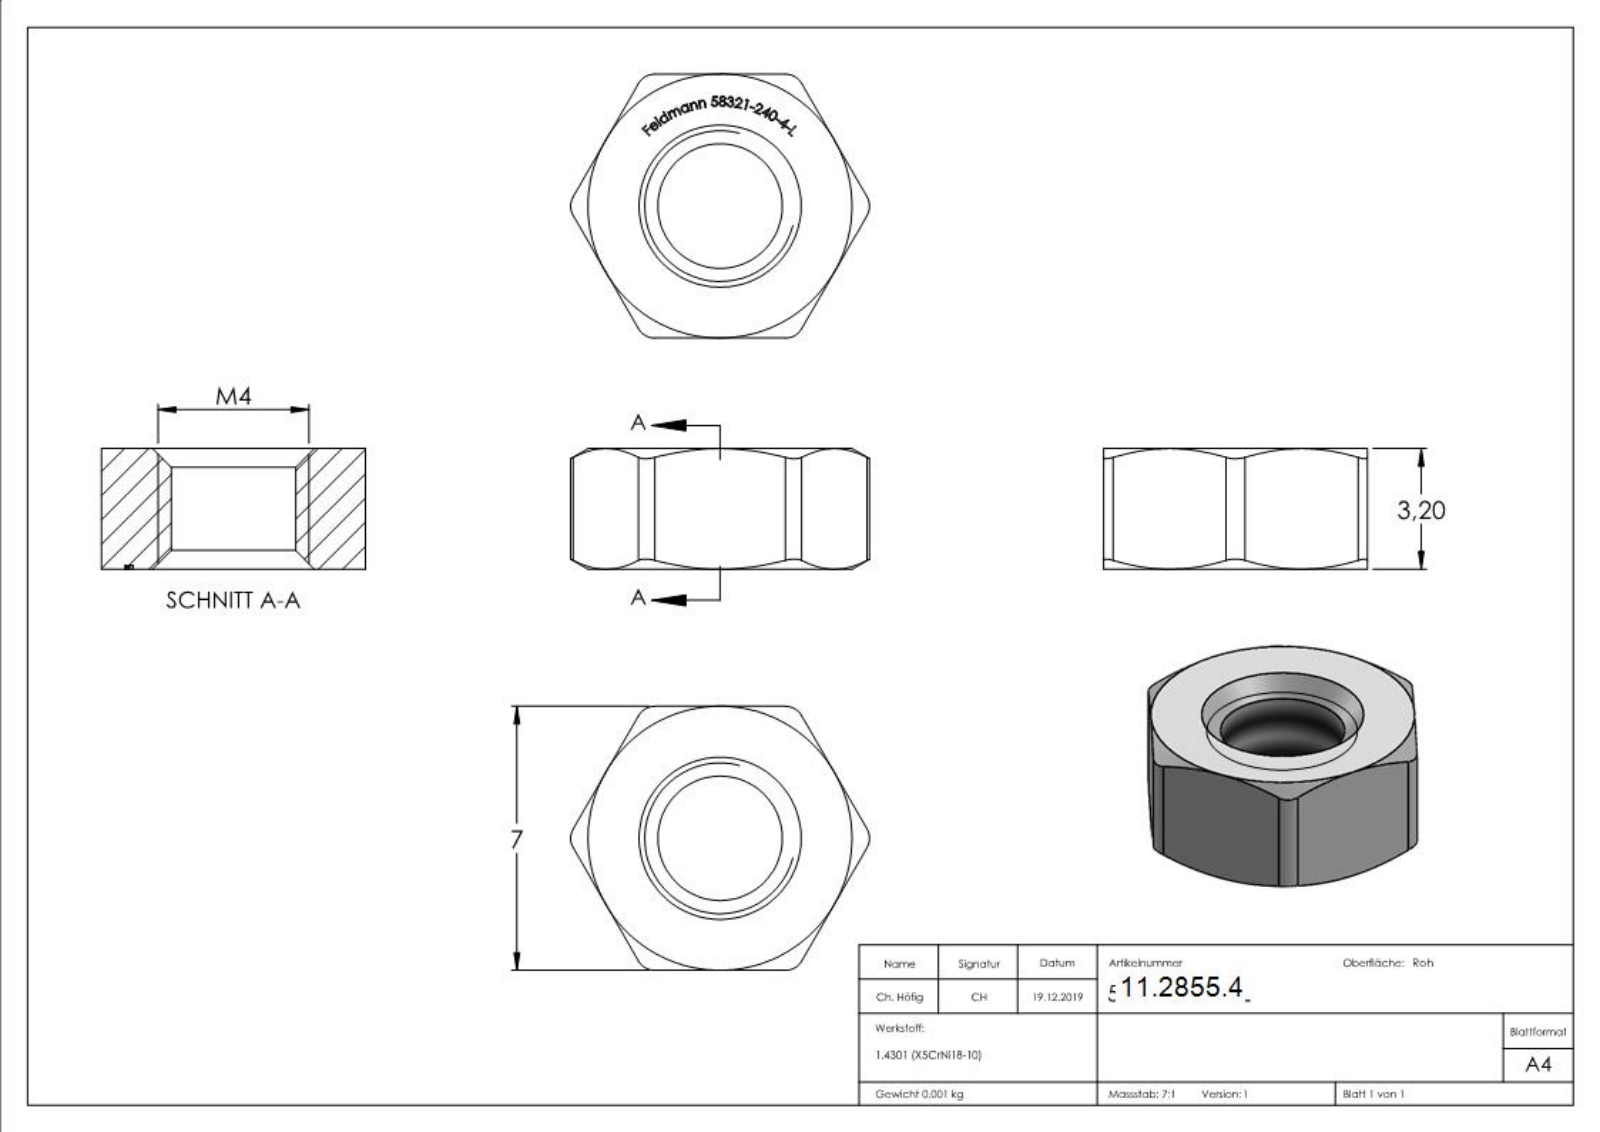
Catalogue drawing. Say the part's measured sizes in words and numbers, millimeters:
The part is named "58321-240-4-L". Its 3-D file was written by "SolidWorks 2015 (CONFIG_CONTROL_DESIGN)". It is 1 solid with 29 faces: 8 planar, 7 cylindrical and 14 other. Overall it measures 22 by 7.93 by 7 millimeters. Its volume is 105 cubic millimeters and its surface area 168 square millimeters. Round holes: 1 of diameter 3.3. Partial cylindrical surfaces (rounded edges, fillets, slot ends): 6 of radius 0.5. The main face-to-face distances are 7, 3.2.
